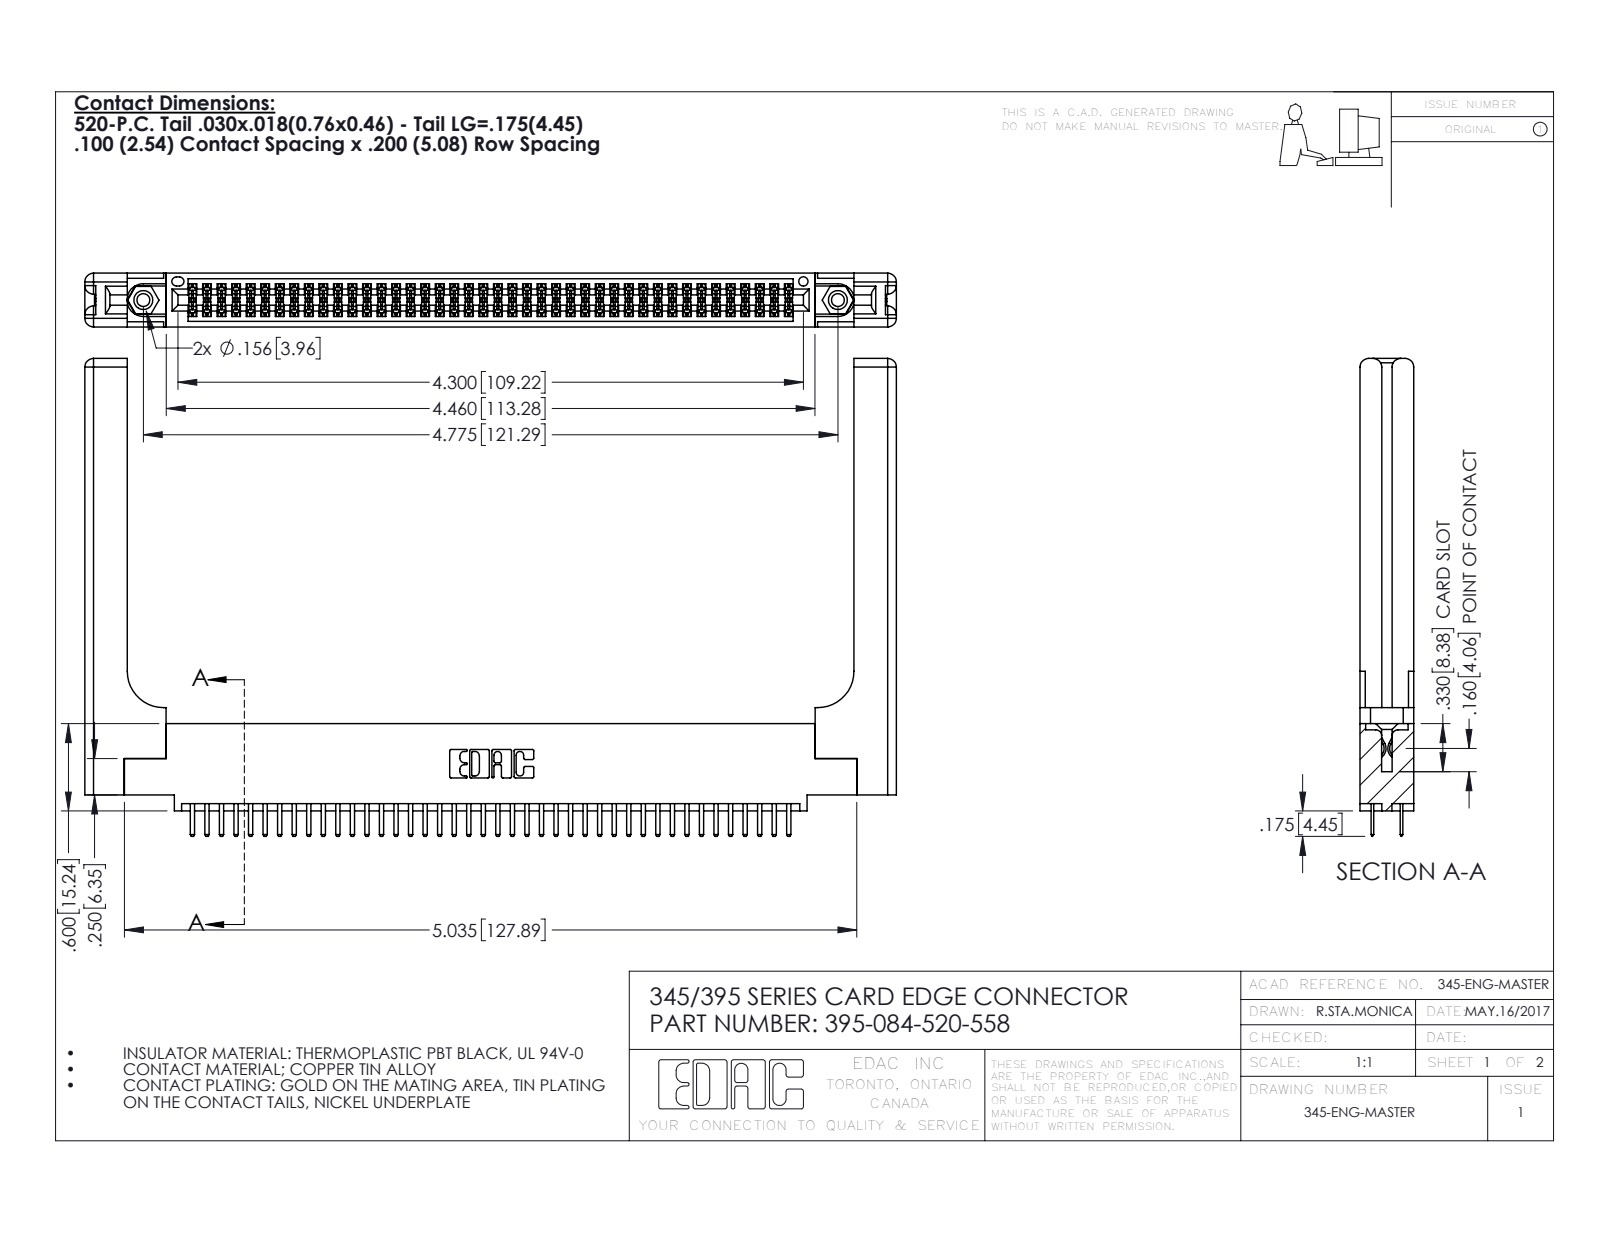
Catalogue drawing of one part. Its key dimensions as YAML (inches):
part_name: "345 Part_0.110 Offset - 0.156 Dia-TH; 345-250-001_345-250-001-102; 395-084-520-558; 345-292-001_345-293-120 (+1 more)"
step_written_by: "SolidWorks 2016 (CONFIG_CONTROL_DESIGN)"
units: inches
bodies: {solids: 89, faces: 4922, planar: 3172, cylindrical: 1690, other: 60}
overall_size: [5.579, 3.285, 0.37]
volume: 1.35
surface_area: 39.15
round_holes:
  - {diameter: 0.089, count: 2}
  - {diameter: 0.125, count: 2}
  - {diameter: 0.156, count: 2}
  - {diameter: 0.064, count: 1}
round_bosses_or_shafts:
  - {diameter: 0.155, count: 2}
partial_cylinders:
  - {radius: 0.006, count: 126}
  - {radius: 0.01, count: 88}
  - {radius: 0.01, count: 22}
  - {radius: 0.06, count: 16}
  - {radius: 0.007, count: 6}
  - {radius: 0.031, count: 6}
  - {radius: 0.026, count: 3}
  - {radius: 0.014, count: 2}
face_to_face_distances: [0.37, 0.072, 0.298, 0.2, 0.098, 0.272, 0.025, 0.225, 0.148, 0.15]
hole_center_spacings: [0.27, 4.539, 4.775]
